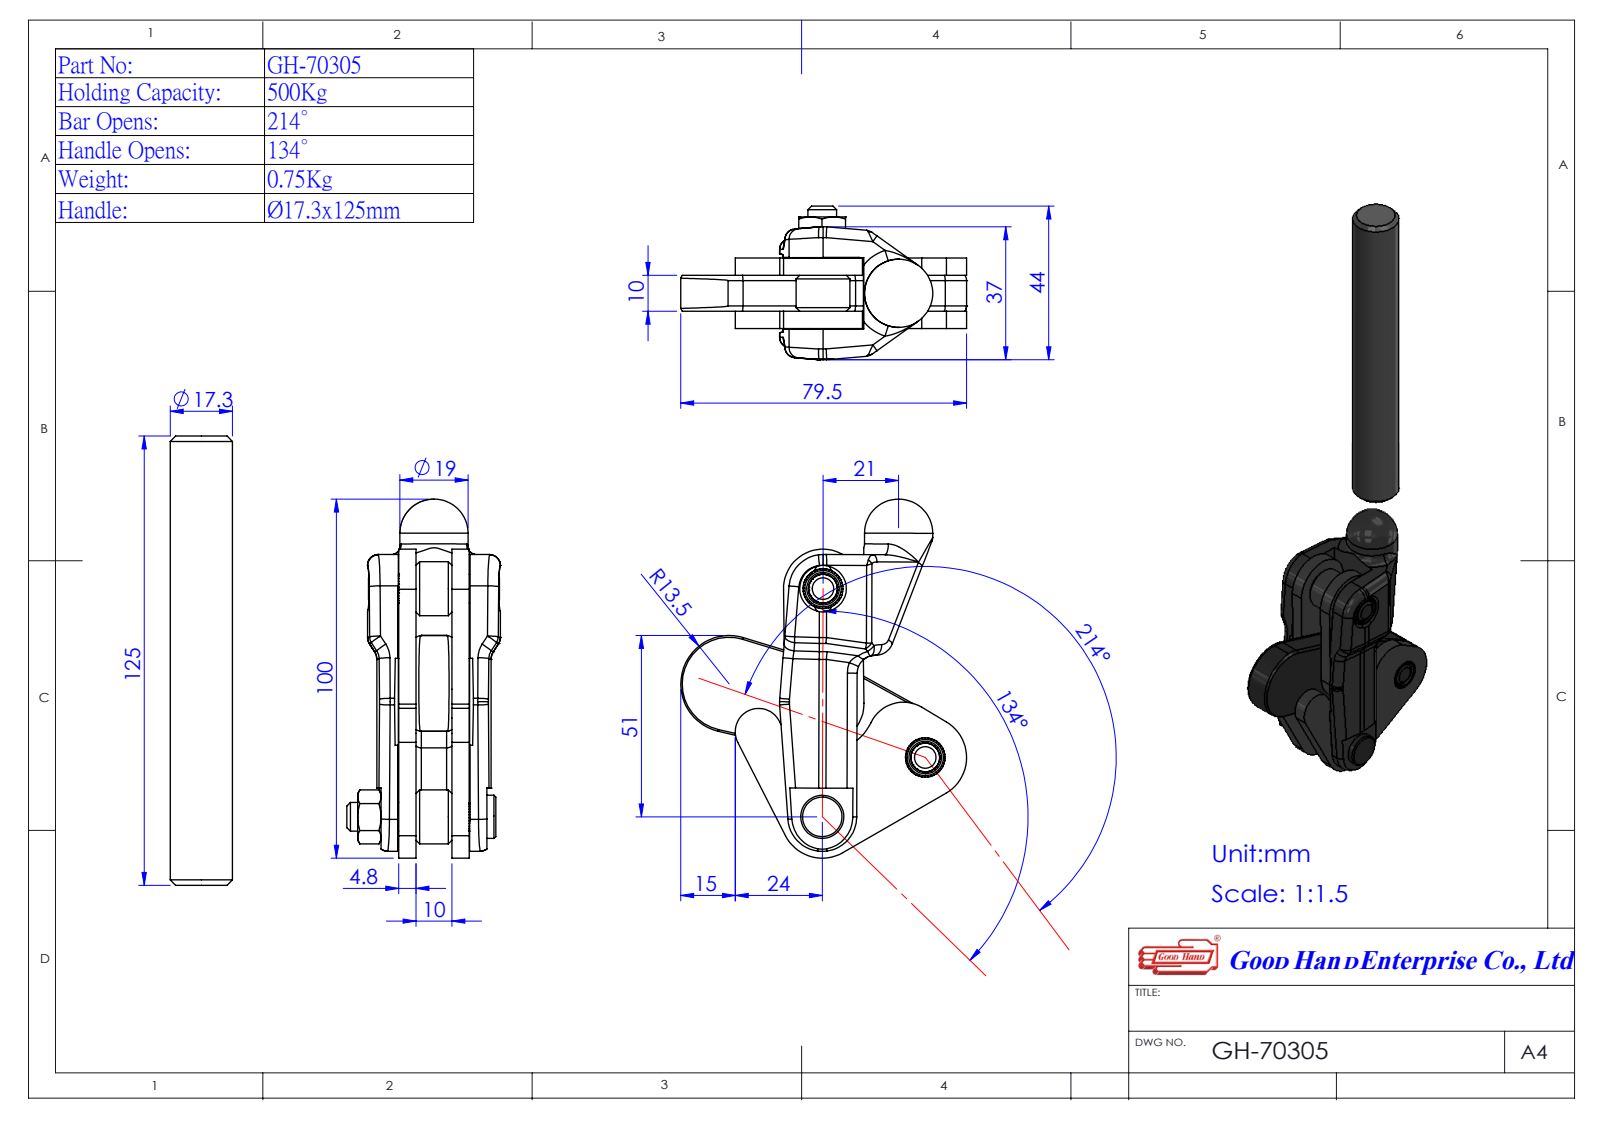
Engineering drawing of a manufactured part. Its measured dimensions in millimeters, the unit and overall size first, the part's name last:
Units: millimetres
Overall size (bounding box): 225.22 × 79.27 × 41.6
Round holes (diameter × count): ⌀8 ×4, ⌀12.5 ×1
Round bosses / shafts (diameter × count): ⌀8.18 ×2, ⌀19 ×1, ⌀17.3 ×1, ⌀15 ×1, ⌀12 ×1, ⌀7.94 ×1
Partial cylindrical surfaces — rounded edges, fillets, slot ends (radius × count): R2 ×22, R5 ×6, R9.5 ×2, R11 ×2, R11.5 ×2, R6.5 ×1, R10 ×1, R12 ×1
Main face-to-face distances: 5, 15, 10, 5.1, 15.1, 4.98, 14.98, 5.02, 15.02, 20
Hole centre spacings: 31.54, 31.81, 32, 33.12, 55.65, 63.5
Volume: 99 368 mm³ · Surface area: 45 676 mm²
Bodies: 5 solids, 206 faces (66 planar, 91 cylindrical, 49 other)
Part name (STEP PRODUCT): Group2^GH-70305(簡化); Group1^GH-70305(簡化); GH-70305(簡化); 17031001-1^GH-70305(簡化) (+2 more)
STEP written by: SolidWorks 2016 (AUTOMOTIVE_DESIGN)
